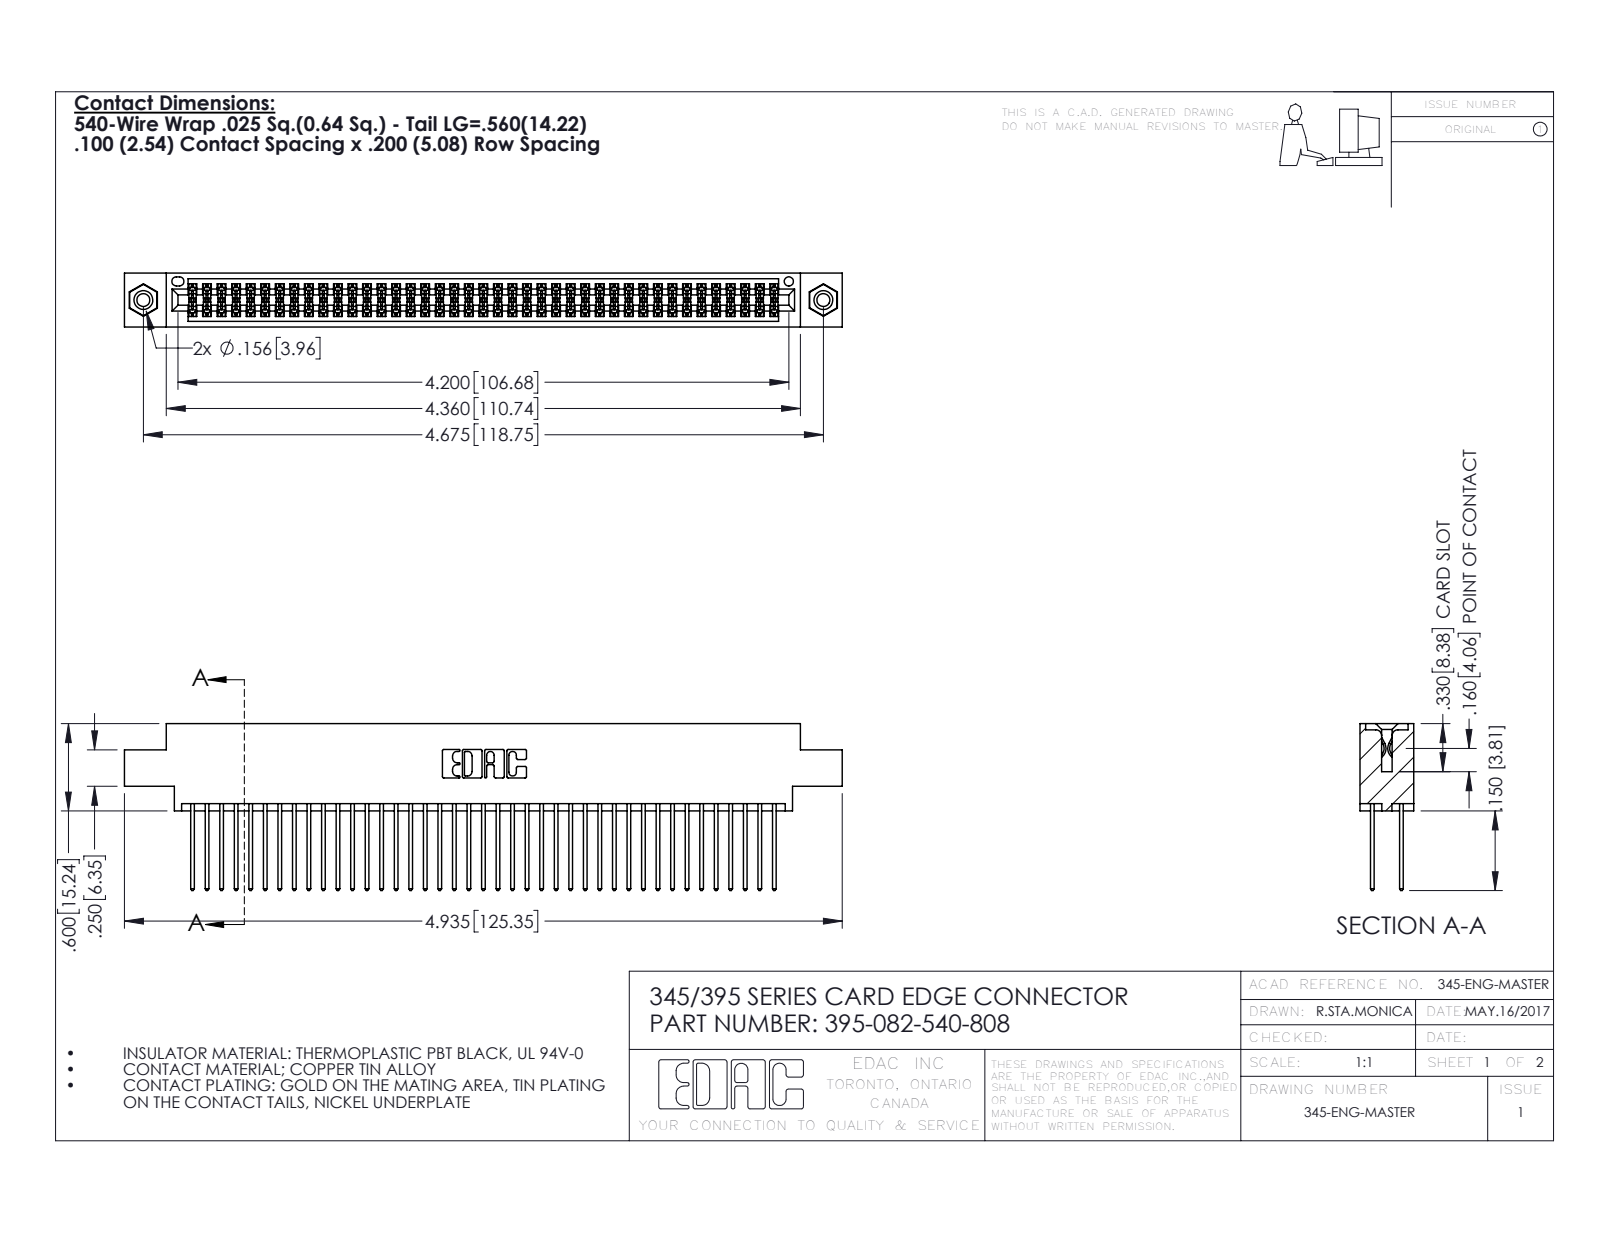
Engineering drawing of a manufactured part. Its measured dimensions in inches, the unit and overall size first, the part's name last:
Units: inches
Overall size (bounding box): 4.935 × 1.147 × 0.37
Round holes (diameter × count): ⌀0.089 ×2, ⌀0.125 ×2, ⌀0.156 ×2, ⌀0.064 ×1
Round bosses / shafts (diameter × count): ⌀0.155 ×2
Partial cylindrical surfaces — rounded edges, fillets, slot ends (radius × count): R0.006 ×123, R0.01 ×82, R0.01 ×22, R0.007 ×6, R0.031 ×6, R0.026 ×3, R0.014 ×2, R0.019 ×2
Main face-to-face distances: 0.072, 0.298, 0.2, 0.098, 0.272, 0.025, 0.37, 0.225, 0.175, 0.149
Hole centre spacings: 0.27, 4.439, 4.675
Volume: 0.754 in³ · Surface area: 30.76 in²
Bodies: 85 solids, 4290 faces (2822 planar, 1452 cylindrical, 16 other)
Part name (STEP PRODUCT): 345-250-001_345-250-003-102; 345-292-001_345-293-140; 395-082-540-808; 345 Part_0.170 Offset - 0.156 Dia-TI
STEP written by: SolidWorks 2016 (CONFIG_CONTROL_DESIGN)
